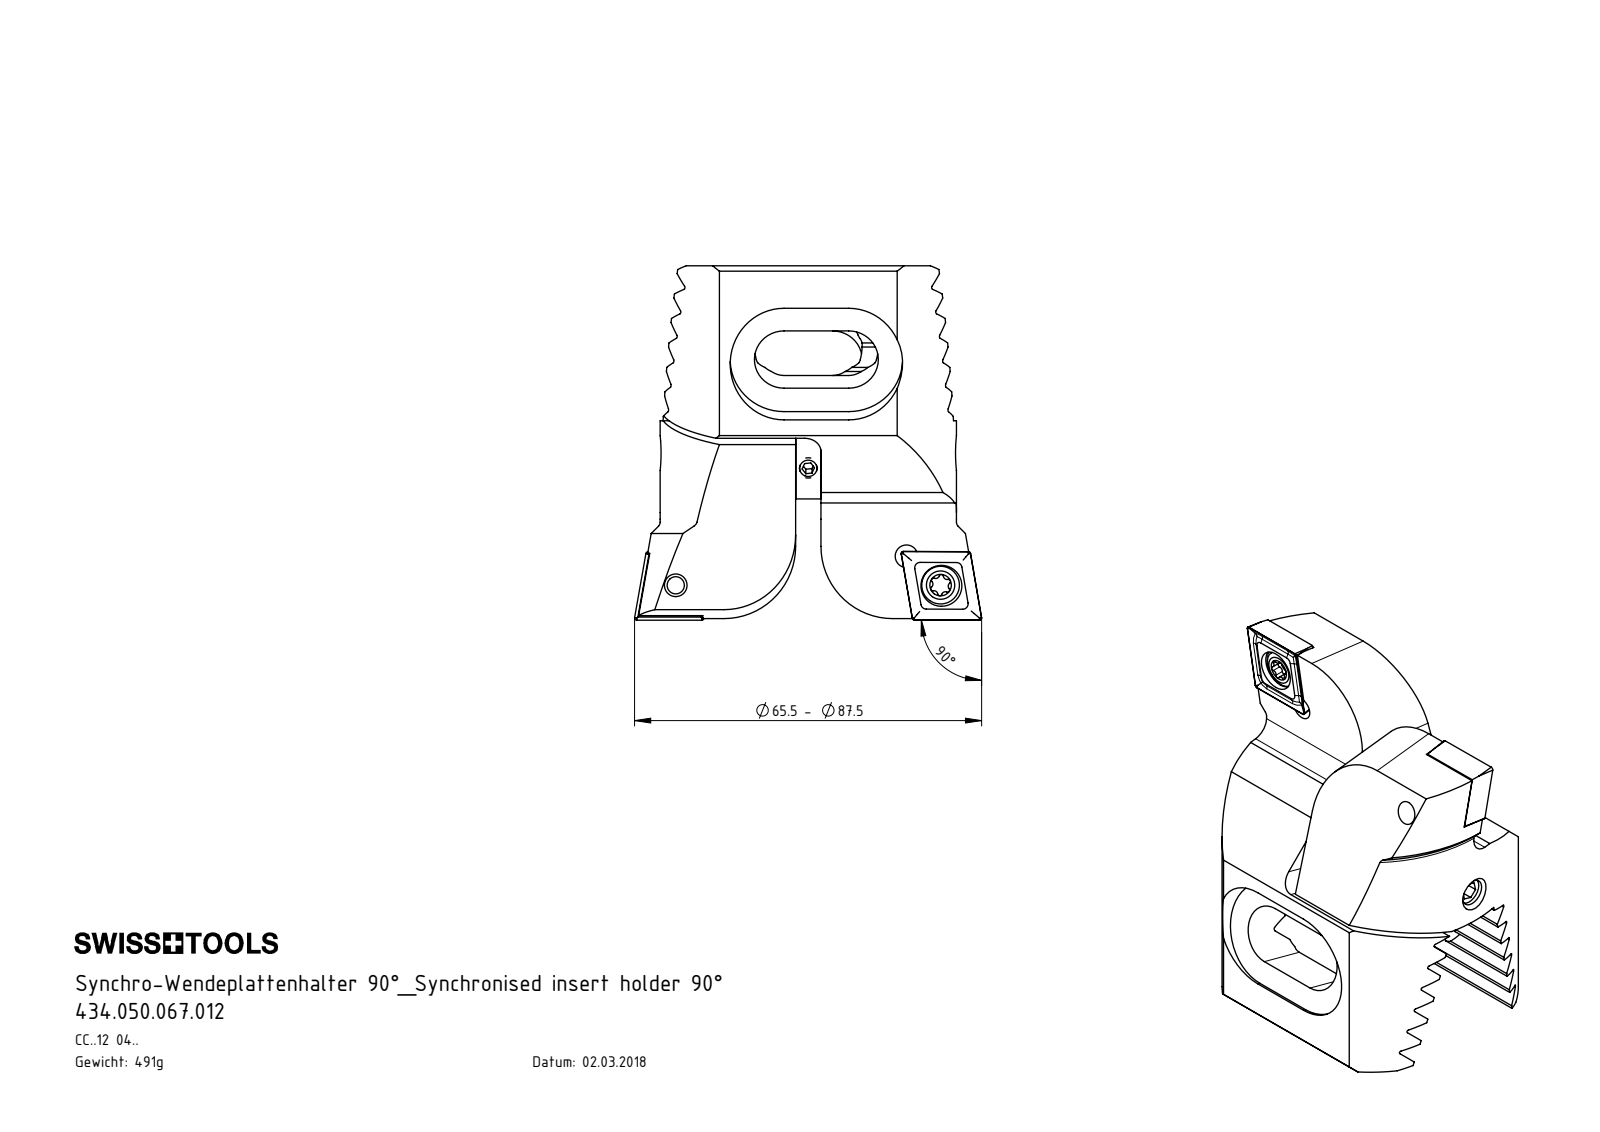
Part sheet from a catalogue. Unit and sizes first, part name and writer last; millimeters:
Units: millimetres
Overall size (bounding box): 65.75 × 64.42 × 44
Round holes (diameter × count): ⌀4.2 ×4, ⌀1 ×3, ⌀3.3 ×3, ⌀5.5 ×2, ⌀7.6 ×2, ⌀5 ×1
Round bosses / shafts (diameter × count): ⌀4 ×3, ⌀7 ×2, ⌀5 ×2, ⌀17 ×1, ⌀6 ×1, ⌀3.8 ×1
Partial cylindrical surfaces — rounded edges, fillets, slot ends (radius × count): R0.34 ×12, R0.39 ×12, R0.69 ×12, R1 ×8, R3 ×4, R5.5 ×4, R10 ×4, R13.3 ×2
Main face-to-face distances: 4.07, 8.14, 12.21, 16.28, 20.35, 4.85, 17.24, 1, 7.12, 21.7
Hole centre spacings: 8.29, 3, 8.49, 8.5, 14.99, 15, 15.3, 28.36
Volume: 62 568 mm³ · Surface area: 24 121 mm²
Bodies: 11 solids, 484 faces (187 planar, 155 cylindrical, 142 other)
Part name (STEP PRODUCT): Z55-WCC.003.037_A; Z42-ER3.002.005_A; Z55-ER3.001.052_A; WCC-ER2.001.010_A (+4 more)
STEP written by: SolidWorks 2017 (CONFIG_CONTROL_DESIGN)
